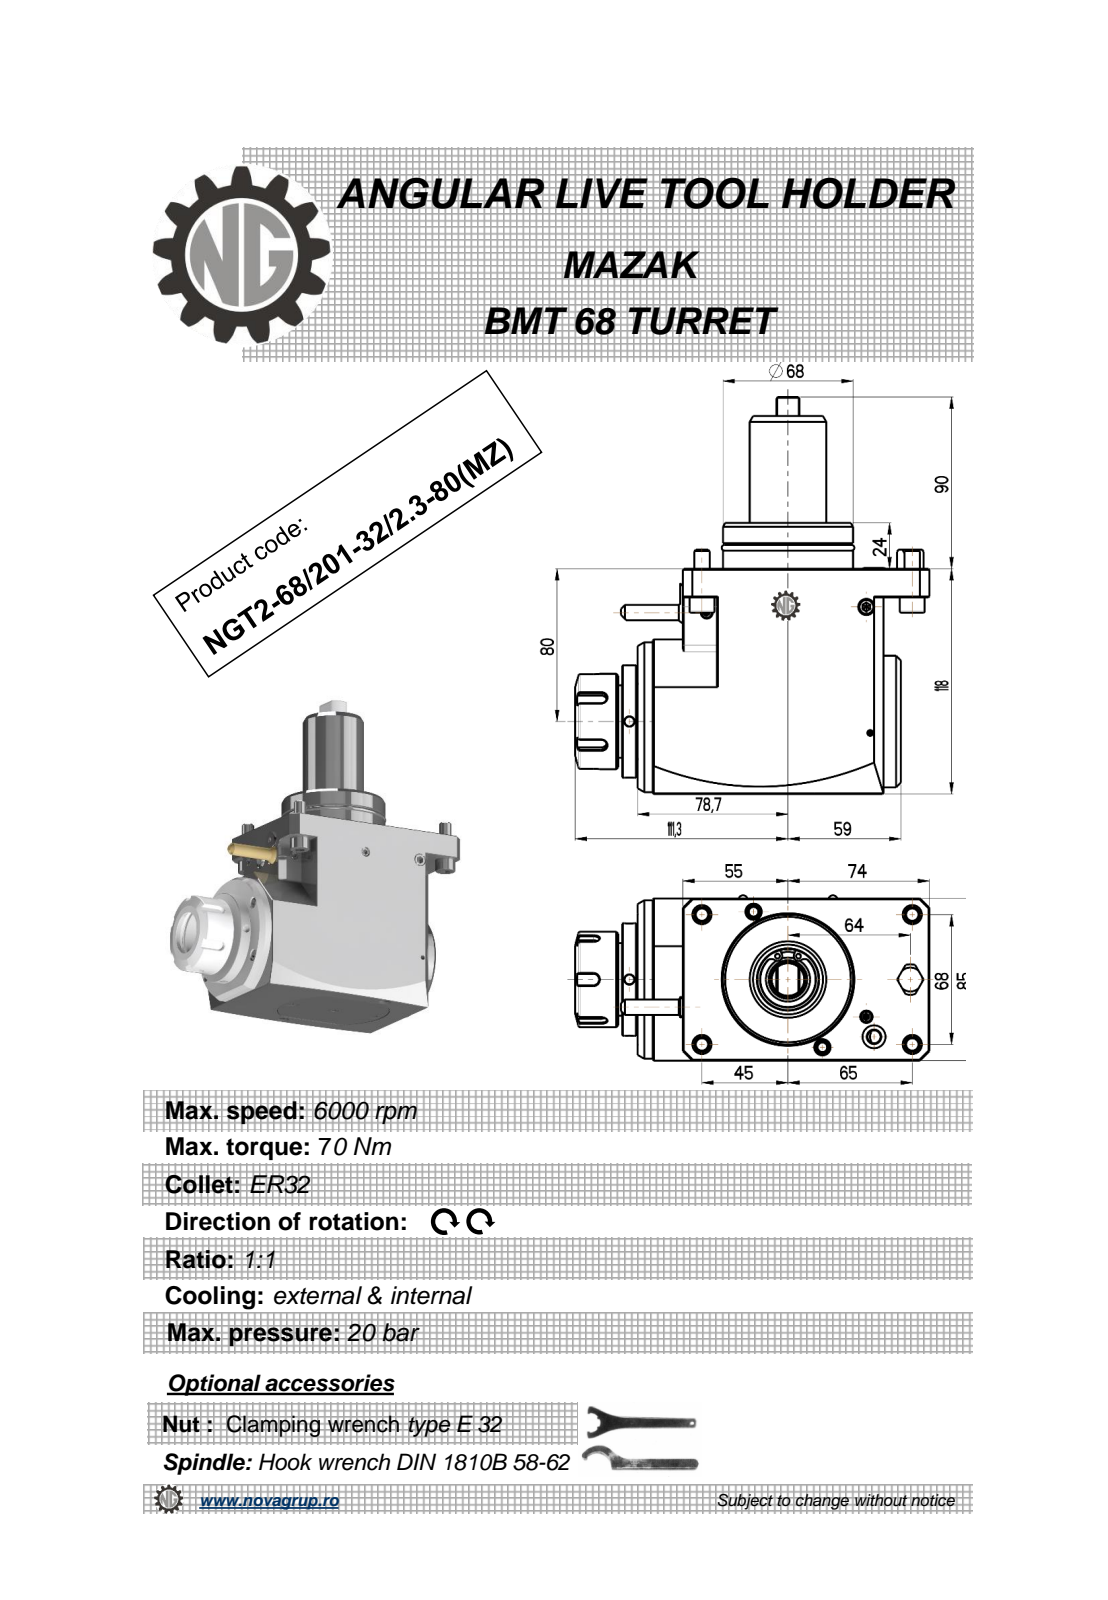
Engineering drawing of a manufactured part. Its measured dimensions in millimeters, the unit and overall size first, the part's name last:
Units: millimetres
Overall size (bounding box): 208 × 185.3 × 86.6
Round holes (diameter × count): ⌀5 ×3, ⌀3 ×1, ⌀6.8 ×1, ⌀27 ×1
Round bosses / shafts (diameter × count): ⌀8 ×5, ⌀13 ×4, ⌀83 ×1, ⌀69 ×1, ⌀68 ×1, ⌀63 ×1, ⌀59 ×1, ⌀50 ×1
Partial cylindrical surfaces — rounded edges, fillets, slot ends (radius × count): R0.22 ×6, R3 ×5, R5 ×4, R0.8 ×2, R550 ×2, R3.4 ×1, R8 ×1, R10 ×1
Main face-to-face distances: 85, 118, 24, 9, 15, 128.7, 137.7, 8, 103, 105
Hole centre spacings: 58.82, 131.42
Volume: 1 453 000 mm³ · Surface area: 104 447 mm²
Bodies: 2 solids, 333 faces (139 planar, 83 cylindrical, 111 other)
Part name (STEP PRODUCT): NGT2_68_201_32_1_3_80_MZ
STEP written by: PRO/ENGINEER BY PARAMETRIC TECHNOLOGY CORPORATION, 2010280 (CONFIG_CONTROL_DESIGN)
